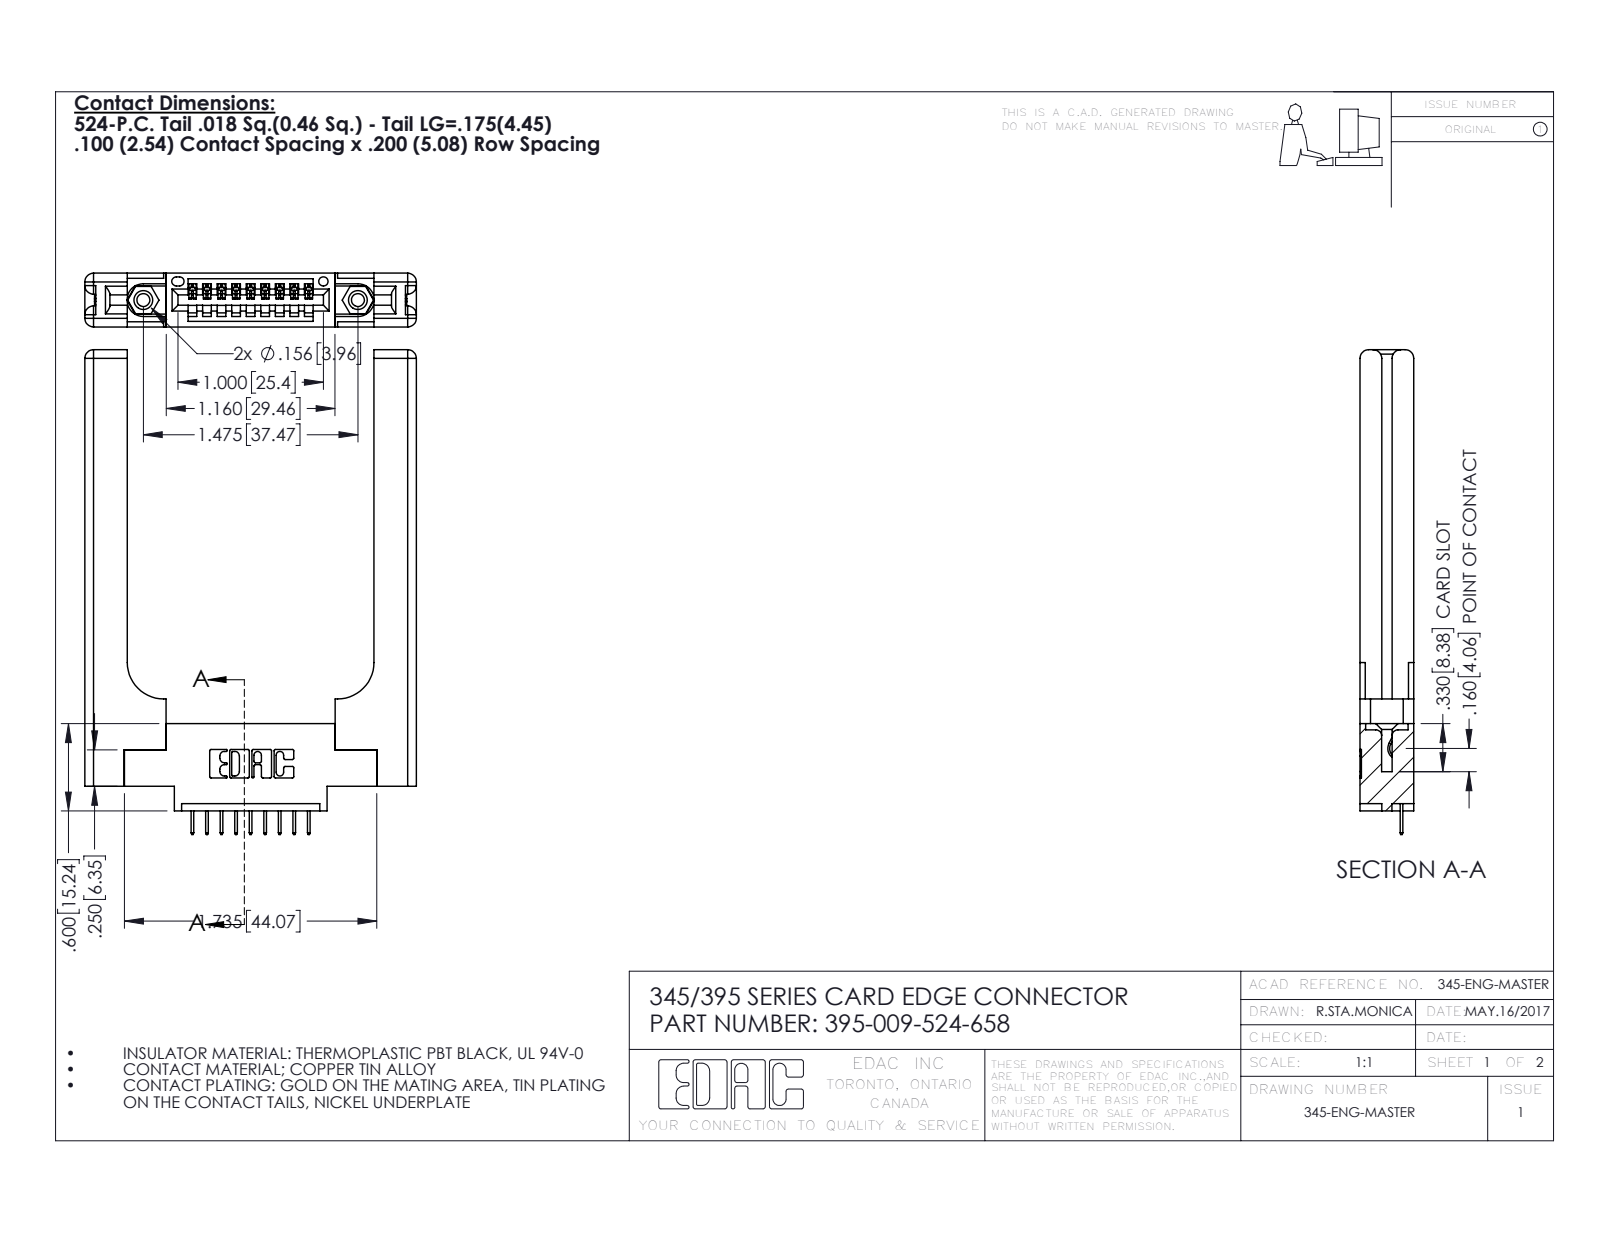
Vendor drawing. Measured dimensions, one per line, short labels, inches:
name: 345-250-001_345-250-001-102; 345-220-058_345-220-058; 345-292-001_345-293-124; 345 Part_0.170 Offset - 0.156 Dia-TH (+1 more)
written by: SolidWorks 2016 (CONFIG_CONTROL_DESIGN)
unit: in
bodies: 14 solids, 944 faces (646 planar, 238 cylindrical, 60 other)
size: 3.332 × 2.279 × 0.37
volume: 0.829 in³; area: 18.01 in²
holes: 2× ⌀0.089, 2× ⌀0.125, 2× ⌀0.156, 1× ⌀0.064
bosses: 2× ⌀0.155
rounds: 22× R0.01, 18× R0.006, 16× R0.06, 6× R0.007, 6× R0.031, 3× R0.026, 2× R0.03, 2× R0.031
face distances: 0.37, 0.15, 0.22, 0.072, 0.148, 0.077, 0.298, 1.696, 0.071, 0.12
hole spacings: 0.27, 1.244, 1.475
